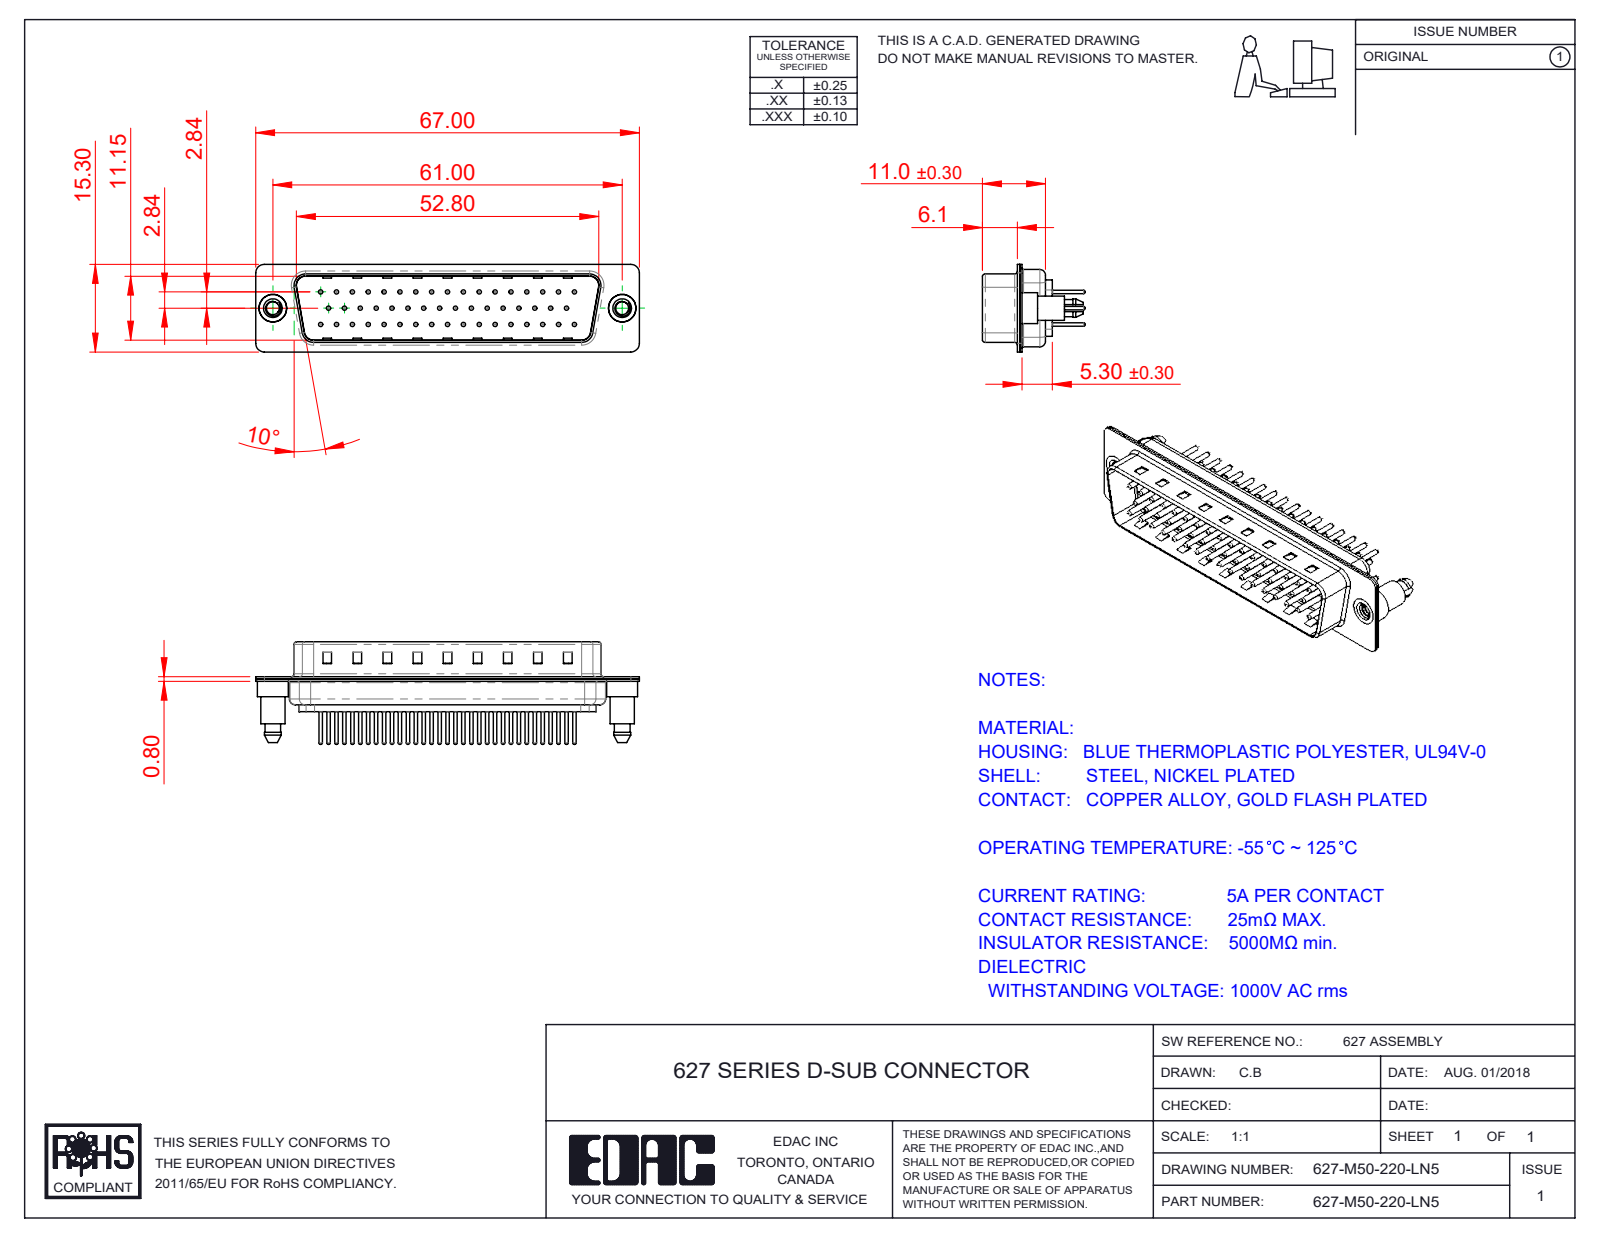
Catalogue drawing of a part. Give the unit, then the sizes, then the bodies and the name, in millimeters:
Units: millimetres
Overall size (bounding box): 67 × 17.9 × 15.3
Round holes (diameter × count): ⌀0.75 ×50, ⌀1.6 ×50, ⌀2 ×50, ⌀2.26 ×2, ⌀4 ×2, ⌀4.8 ×2
Round bosses / shafts (diameter × count): ⌀1.5 ×50, ⌀0.6 ×50, ⌀5.4 ×2, ⌀4.9 ×2, ⌀4.25 ×2
Partial cylindrical surfaces — rounded edges, fillets, slot ends (radius × count): R1.5 ×18, R2 ×12, R1.6 ×10, R0.5 ×8, R0.25 ×4, R0.6 ×4, R0.65 ×4, R0.9 ×4
Main face-to-face distances: 0.4, 11.55, 5.7, 6.1, 0.78, 0.77, 12.33, 5.3, 12.32, 13.1
Hole centre spacings: 3.16, 2.77, 5.54, 8.31, 11.08, 13.85, 16.62, 5.03
Volume: 4 659 mm³ · Surface area: 11 032 mm²
Bodies: 55 solids, 2312 faces (569 planar, 873 cylindrical, 870 other)
Part name (STEP PRODUCT): 627M Housing_50 Contacts; 627M Contact Row 3_20; 627M Contact Row 1_20; 627M Shell Front_50 Contacts (+4 more)
STEP written by: SolidWorks 2020 (CONFIG_CONTROL_DESIGN)
